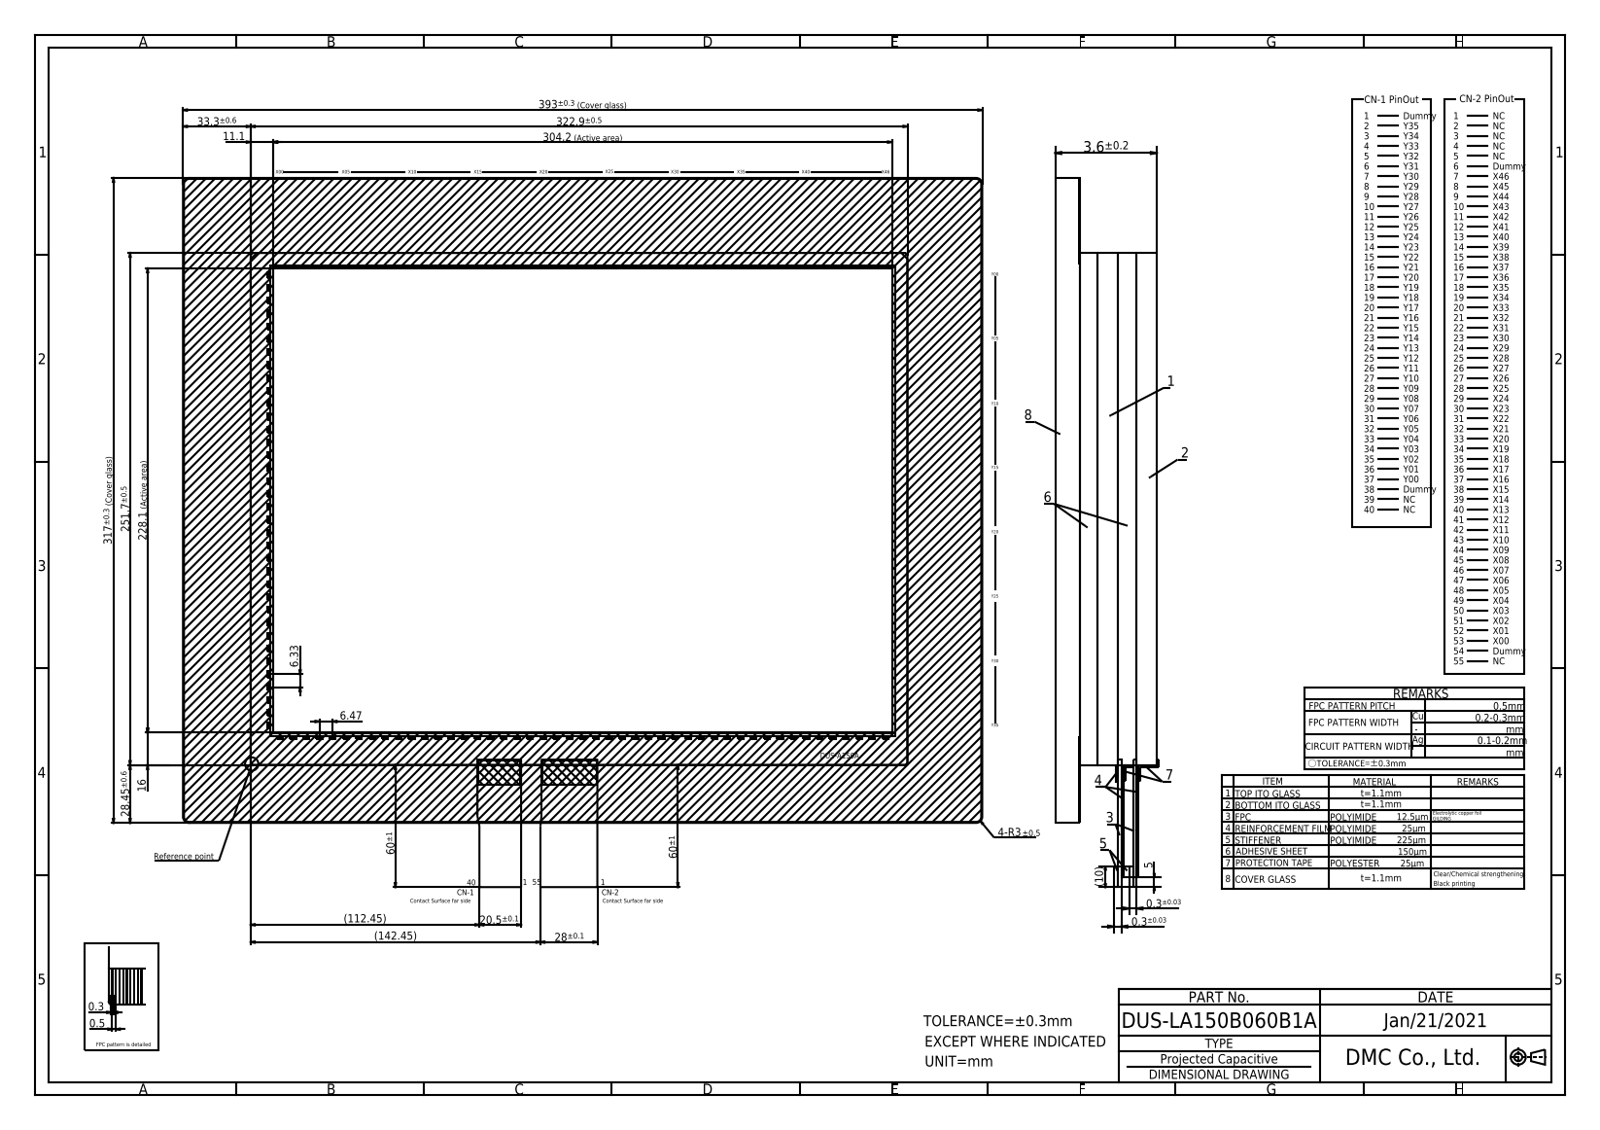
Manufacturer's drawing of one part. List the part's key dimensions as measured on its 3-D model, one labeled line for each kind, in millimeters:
Part name (STEP PRODUCT): DUS-LA150B060B1A
STEP written by: Autodesk Inventor 2020 (CONFIG_CONTROL_DESIGN)
Units: millimetres
Bodies: 1 solid, 425 faces (420 planar, 5 cylindrical, 0 other)
Overall size (bounding box): 550.2 × 443.8 × 3.6
Volume: 333 689 mm³ · Surface area: 398 378 mm²
Partial cylindrical surfaces — rounded edges, fillets, slot ends (radius × count): R3 ×4, R0.2 ×1
Main face-to-face distances: 1.1, 2.5, 3.6, 1.2, 2.4, 1.25, 1.15, 1.35, 2.45, 2.35
